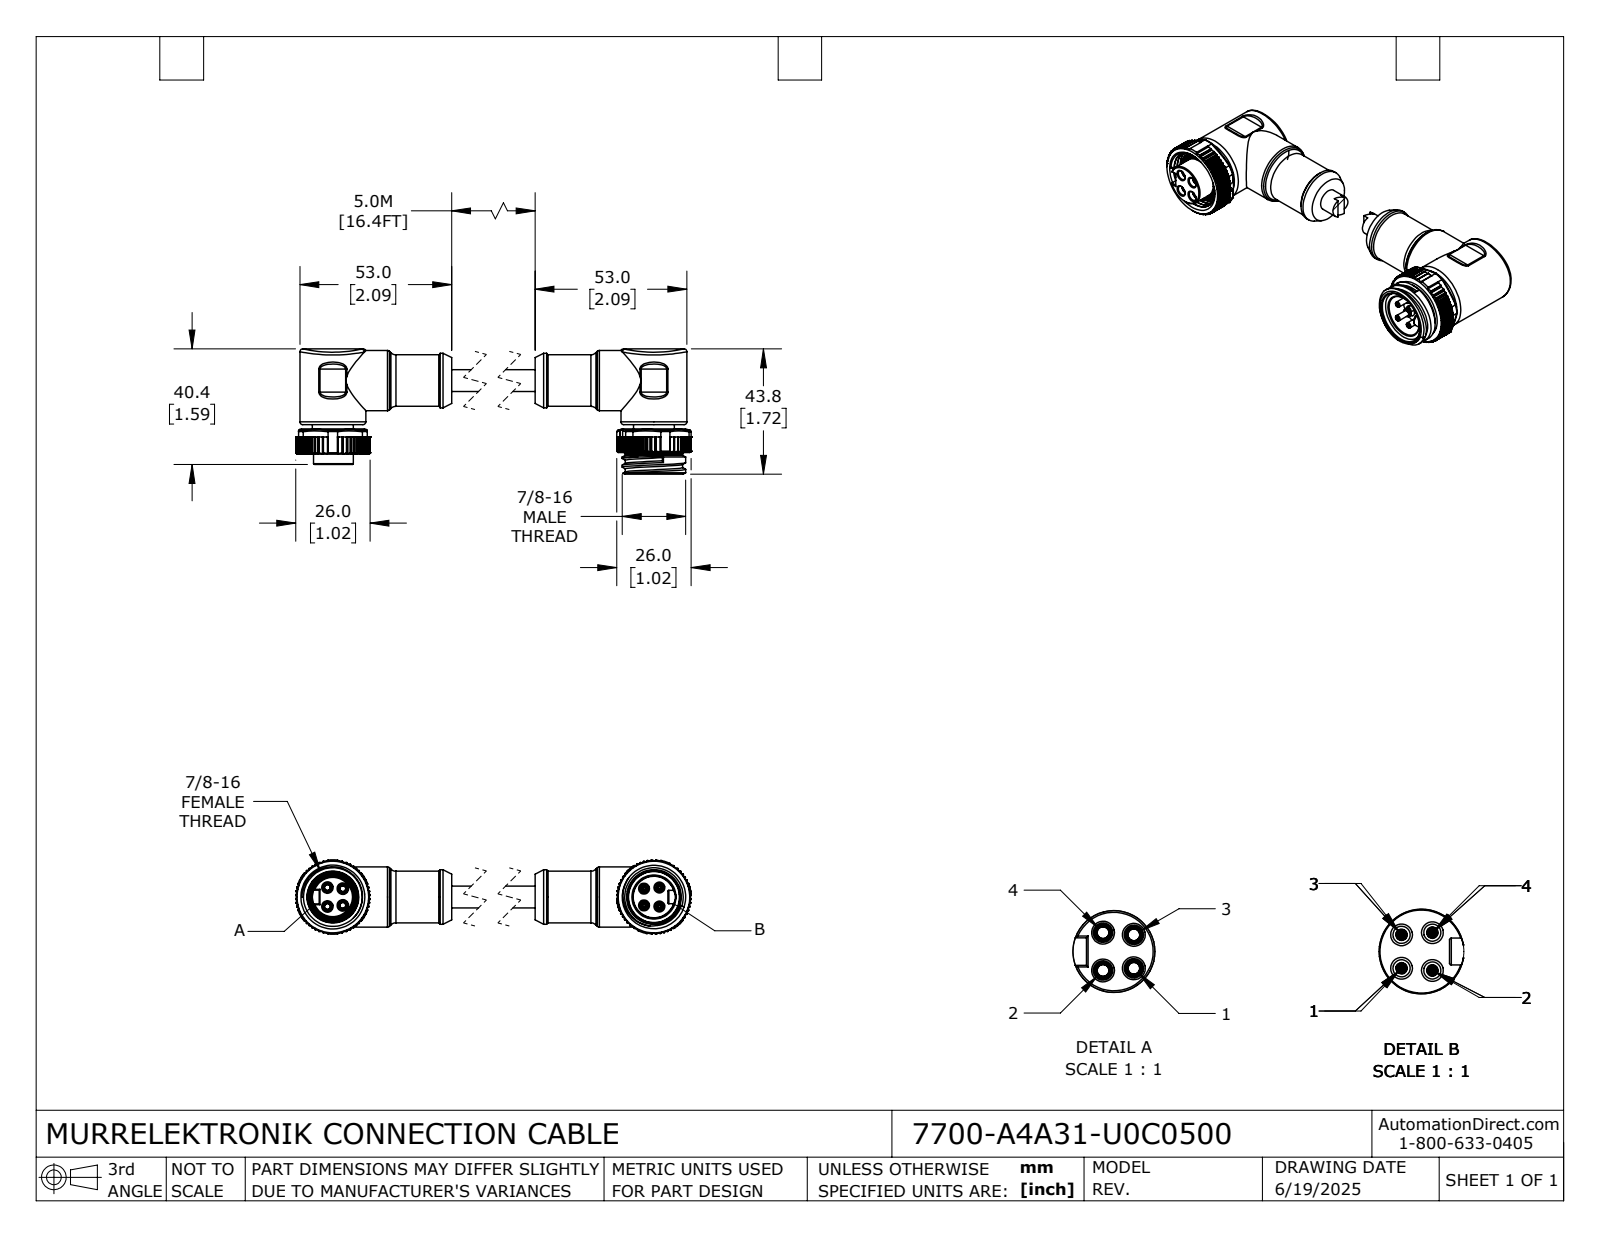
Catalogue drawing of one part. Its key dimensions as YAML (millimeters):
part_name: "7700-A4A31-U0C0500_FEMALE; 7700-A4A31-U0C0500; 7700-A4A31-U0C0500_MALE"
step_written_by: "SolidWorks 2024 (CONFIG_CONTROL_DESIGN)"
units: millimeters
bodies: {solids: 2, faces: 1268, planar: 520, cylindrical: 581, other: 167}
overall_size: [138.97, 43.76, 26]
volume: 49781
surface_area: 17240
round_holes:
  - {diameter: 2.05, count: 4}
  - {diameter: 3, count: 4}
  - {diameter: 3.4, count: 4}
  - {diameter: 15.6, count: 2}
  - {diameter: 15.5, count: 1}
  - {diameter: 18.5, count: 1}
  - {diameter: 20.5, count: 1}
  - {diameter: 22.22, count: 1}
round_bosses_or_shafts:
  - {diameter: 3, count: 4}
  - {diameter: 2, count: 4}
  - {diameter: 23, count: 2}
  - {diameter: 18.1, count: 2}
  - {diameter: 17.8, count: 2}
  - {diameter: 14.3, count: 2}
  - {diameter: 22.17, count: 1}
  - {diameter: 21, count: 1}
partial_cylinders:
  - {radius: 0.2, count: 252}
  - {radius: 0.3, count: 34}
  - {radius: 0.1, count: 8}
  - {radius: 1, count: 8}
  - {radius: 0.7, count: 4}
  - {radius: 0.73, count: 4}
  - {radius: 2.5, count: 4}
  - {radius: 13, count: 2}
face_to_face_distances: [1.5, 8.8, 7.3, 9.7, 0.9, 7, 30, 8.2, 21, 4.2]
hole_center_spacings: [3.81, 4.54, 5.39, 8.22, 109.56, 114.95, 5.84, 6.6]
